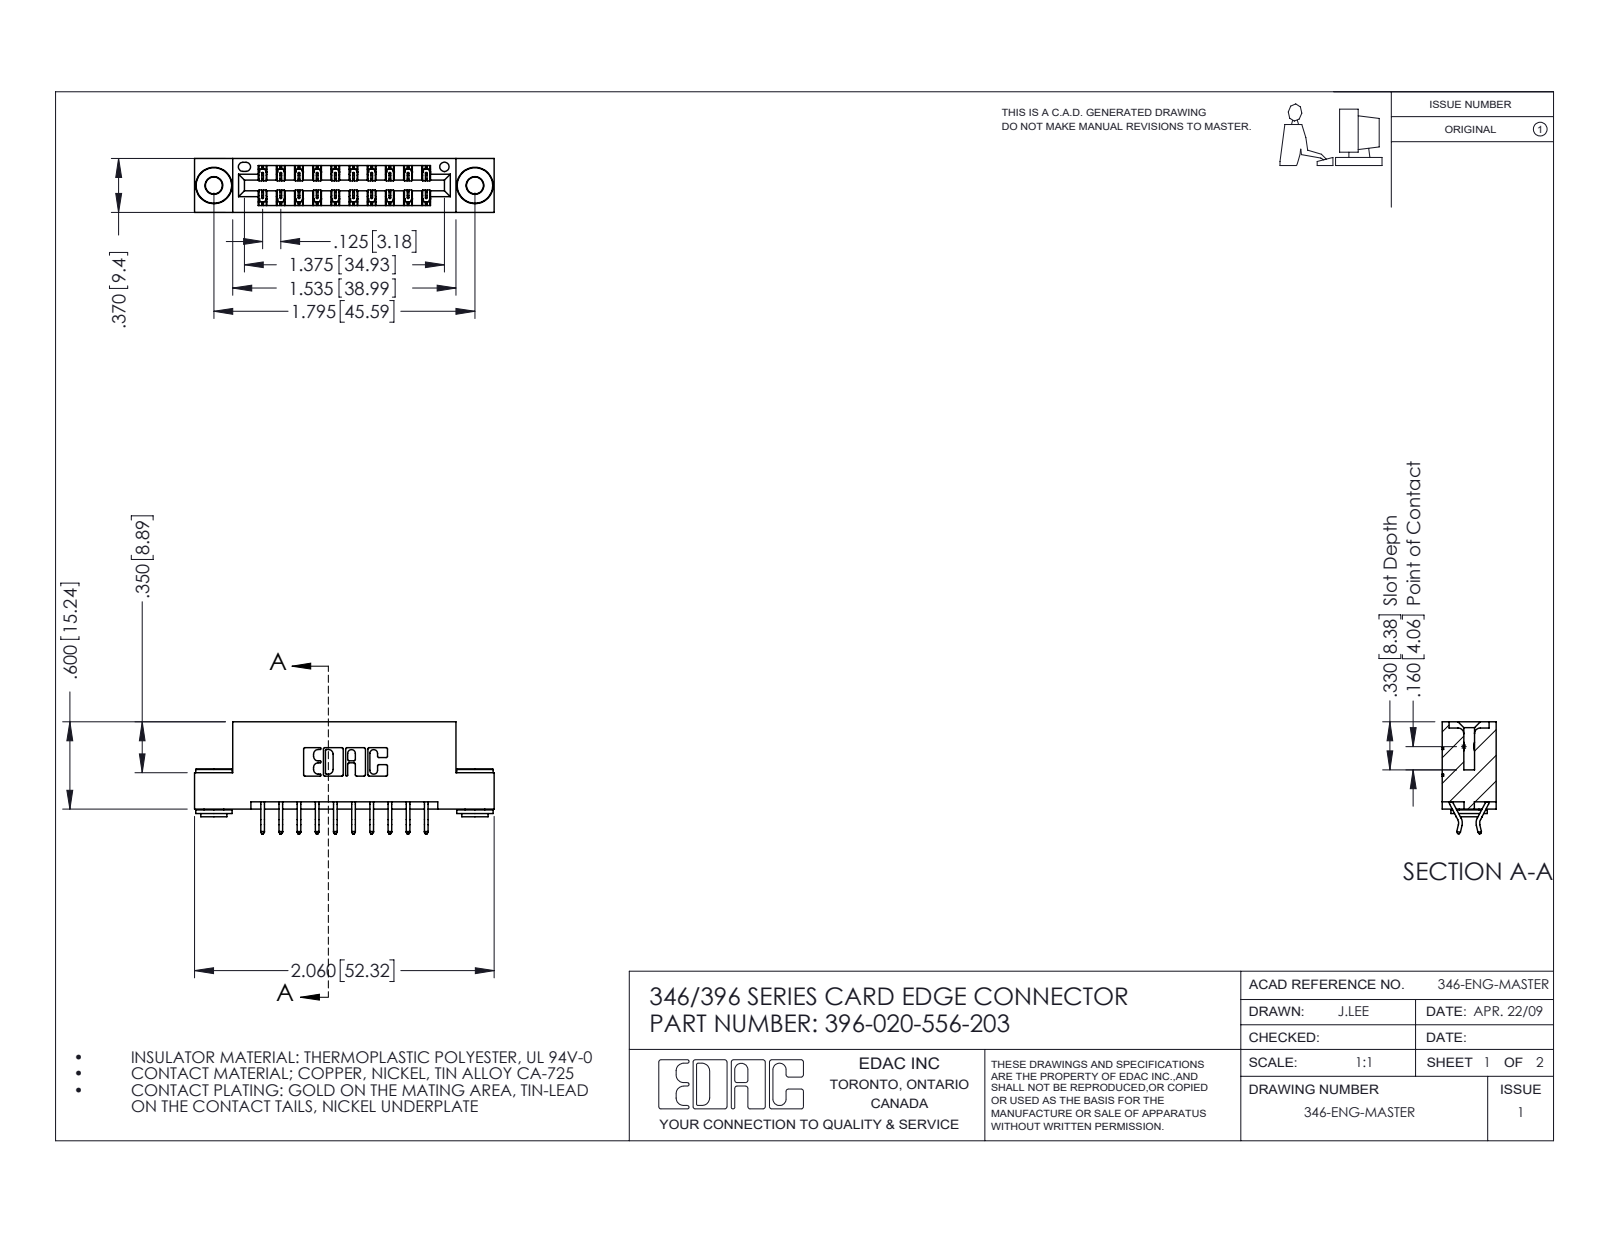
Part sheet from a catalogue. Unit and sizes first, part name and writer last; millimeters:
Units: millimetres
Overall size (bounding box): 52.3 × 19.6 × 9.4
Round holes (diameter × count): ⌀2.9 ×2, ⌀4 ×2, ⌀1.6 ×1
Round bosses / shafts (diameter × count): ⌀6.4 ×2, ⌀4.6 ×2, ⌀3.5 ×2
Partial cylindrical surfaces — rounded edges, fillets, slot ends (radius × count): R0.2 ×30, R0.3 ×22, R0.2 ×6, R0.8 ×6, R0.7 ×3, R0.3 ×2, R0.4 ×2, R0.6 ×2
Main face-to-face distances: 6.4, 1.2, 8.2, 9.4, 0.6, 1.8, 7.6, 3.8, 5.6, 2.5
Hole centre spacings: 6.2, 40.4, 45.6
Volume: 4 870 mm³ · Surface area: 6 390 mm²
Bodies: 23 solids, 1320 faces (866 planar, 446 cylindrical, 8 other)
Part name (STEP PRODUCT): 345-292-001_556 Tail; 396-020-556-203; 346 Part_Flush Mounting Lugs - 0.156 Dia-TH; 345-250-002_345-250-002-102
STEP written by: SolidWorks 2016 (CONFIG_CONTROL_DESIGN)
